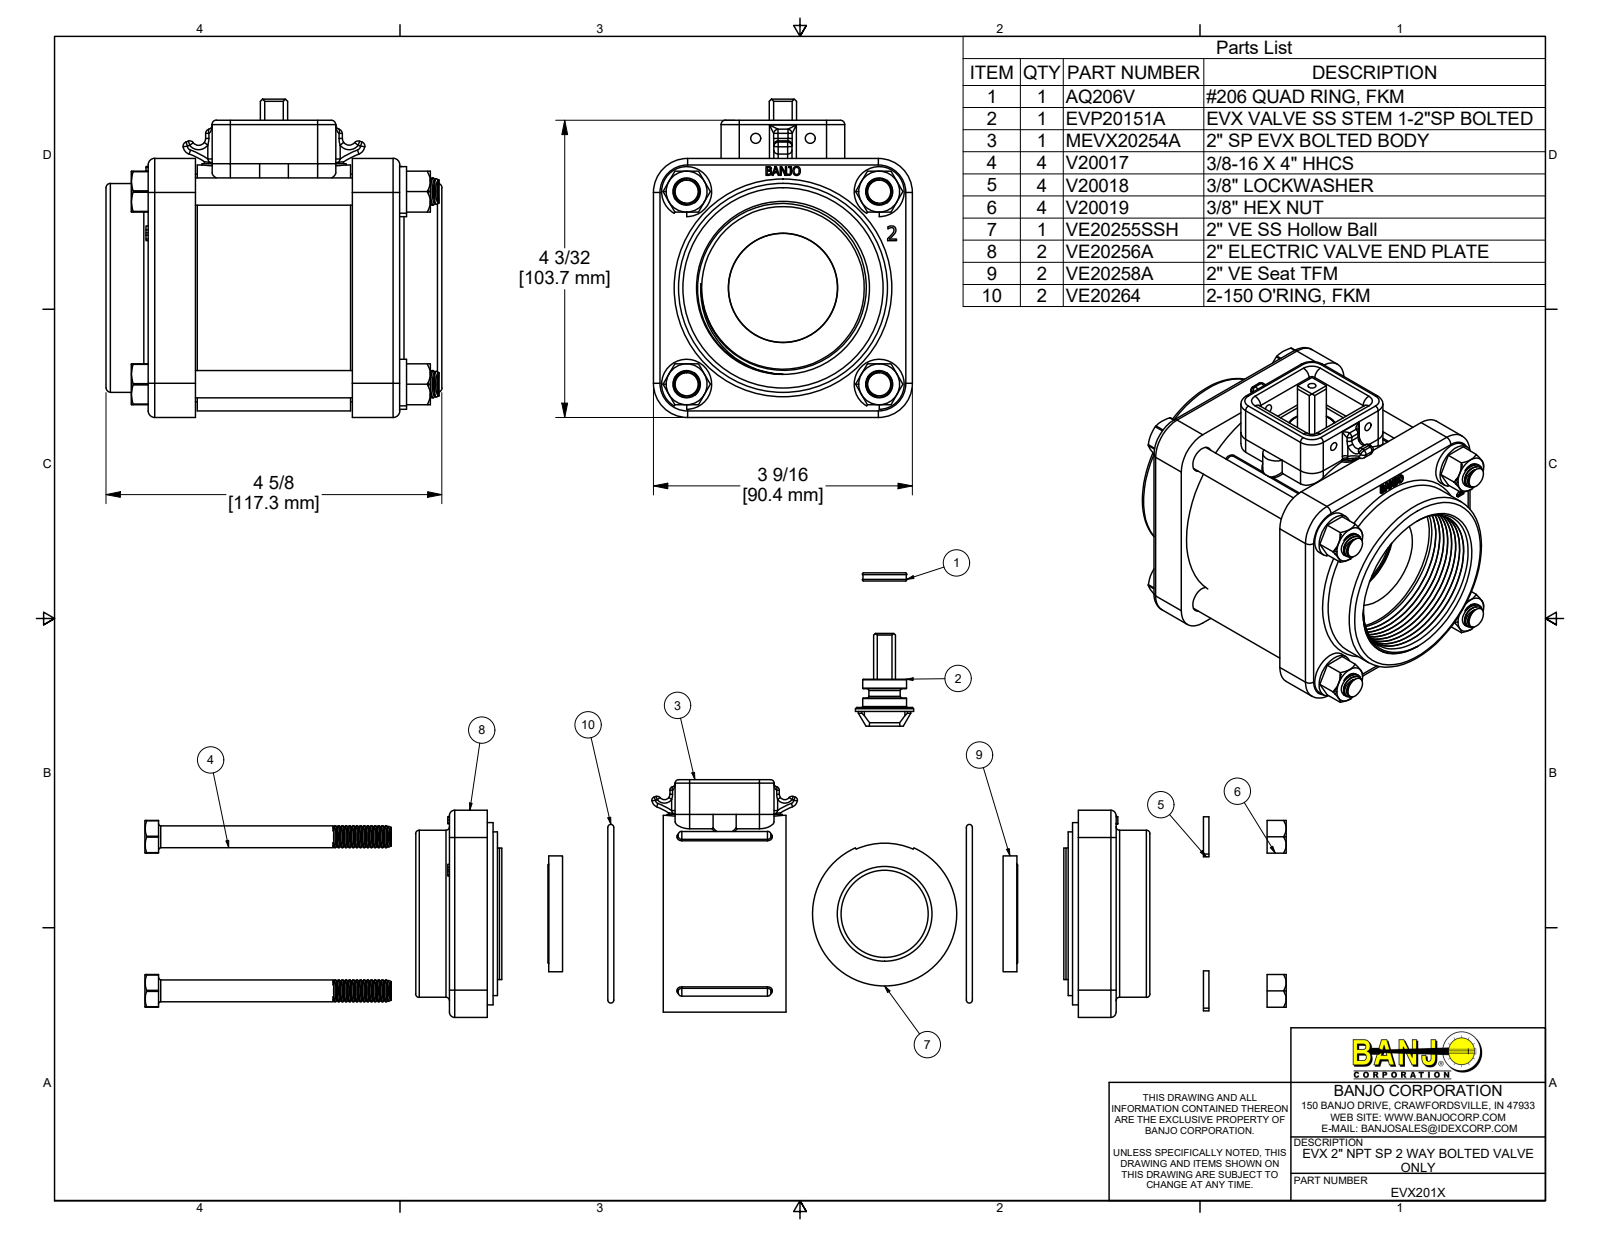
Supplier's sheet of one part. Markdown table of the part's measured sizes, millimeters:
| quantity | value |
| --- | --- |
| part name | EVX201X; MEVX20254A; MEVX20254AX; V20017 (+8 more) |
| STEP written by | Autodesk Inventor 2019 (AUTOMOTIVE_DESIGN) |
| units | millimeters |
| bodies | 22 solids, 1269 faces (336 planar, 400 cylindrical, 533 other) |
| overall size | 117.3 × 111.1 × 90.4 |
| volume | 472 600 mm³ |
| surface area | 163 400 mm² |
| round holes (diameter × count) | 7.8 × 4, 9.8 × 4, 10.3 × 4, 3.4 × 2, 38.1 × 2, 19.3 × 1, 25.9 × 1, 38 × 1, 50.7 × 1, 56.8 × 1, 65 × 1, 77.8 × 1 |
| round bosses / shafts (diameter × count) | 8.2 × 60, 17.4 × 4, 9.5 × 4, 85.9 × 1, 79.5 × 1, 72.9 × 1, 71.4 × 1, 57.4 × 1 |
| partial cylindrical surfaces (radius × count) | 1.5 × 28, 2.3 × 12, 0.5 × 8, 4.1 × 8, 3.2 × 6, 0.4 × 4, 0.8 × 4, 5.3 × 4 |
| main face-to-face distances | 16.5, 71.3, 21, 66.9, 4.4, 50.4, 90.4, 9.4, 7.1, 80.7 |
| hole center spacings | 47.5, 67.3, 30.4, 47, 53, 89.1, 95.1, 96 |
